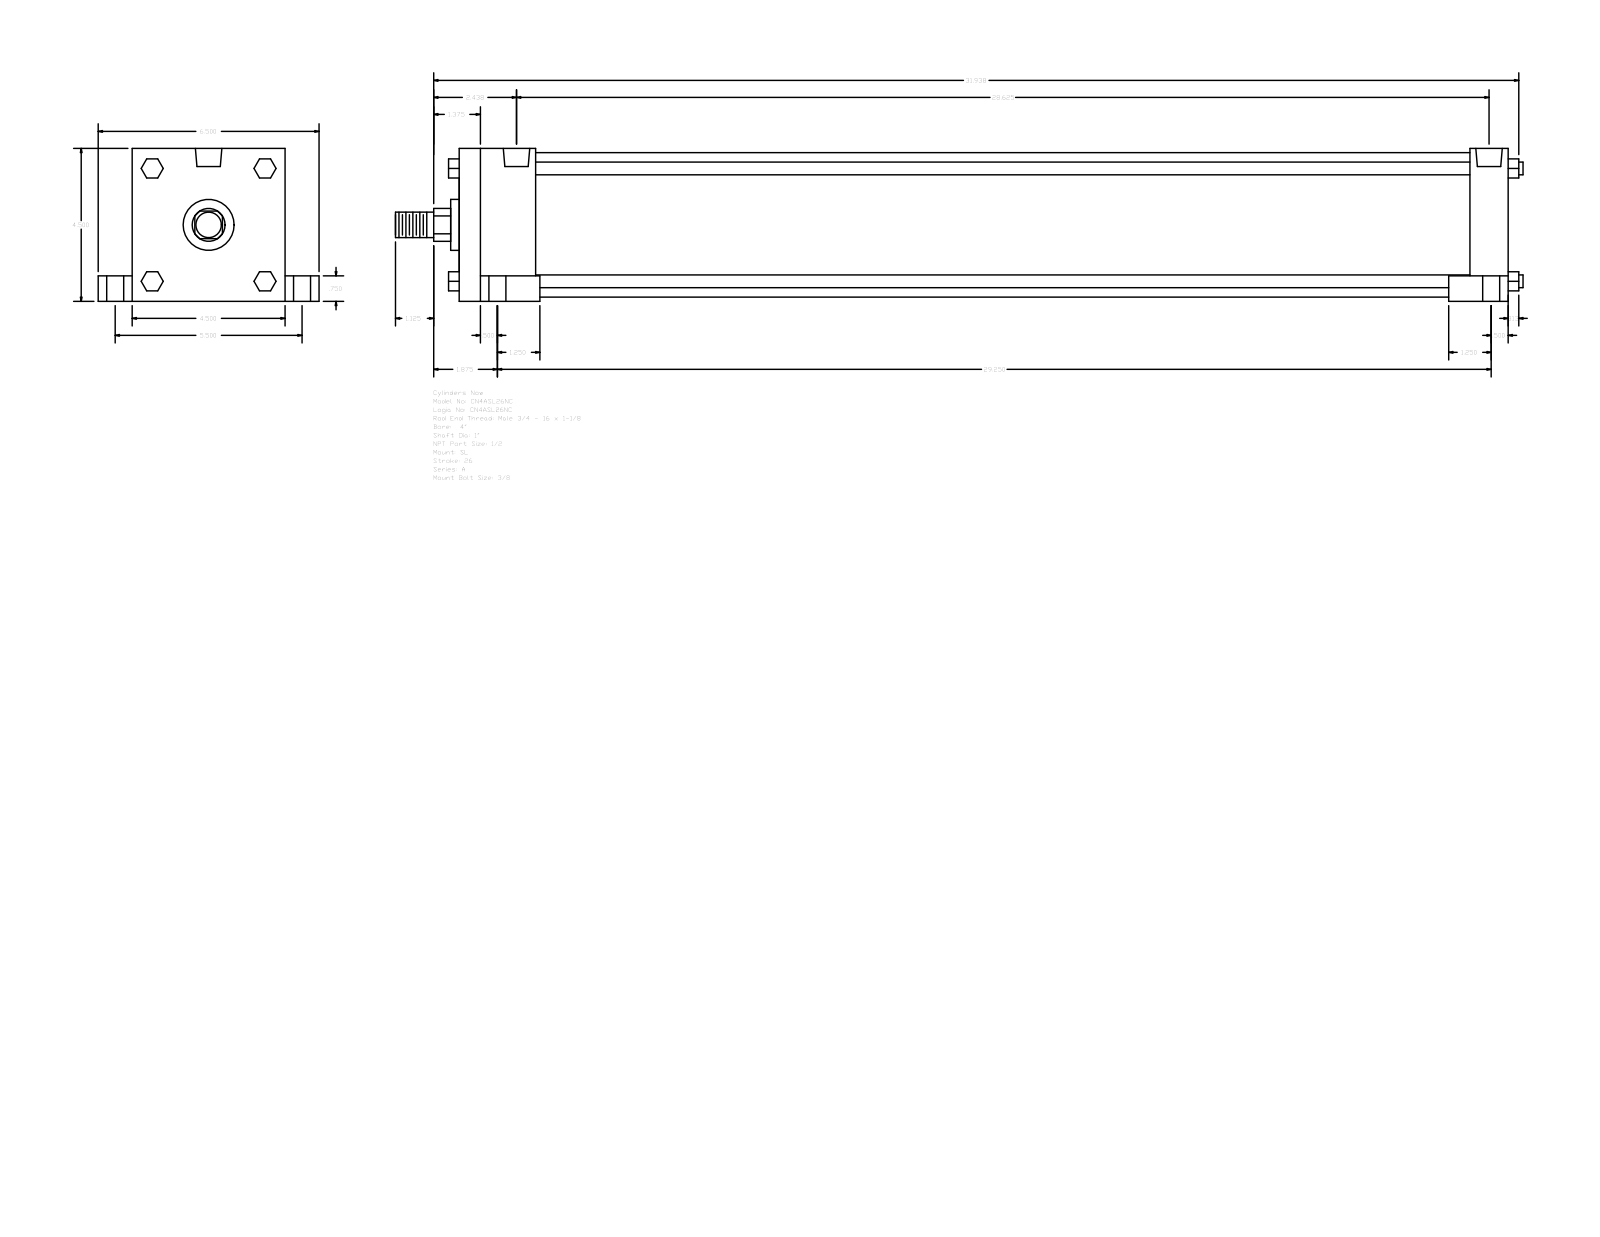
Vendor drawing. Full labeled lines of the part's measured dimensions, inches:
Part name (STEP PRODUCT): A_SL__0400_1
STEP written by: GSSL Pune (CONFIG_CONTROL_DESIGN)
Units: inches
Bodies: 0 solids, 150 faces (114 planar, 36 cylindrical, 0 other)
Overall size (bounding box): 33.187 × 6.5 × 4.5
Round holes (diameter × count): ⌀0.344 ×4, ⌀0.5 ×4, ⌀0.75 ×4, ⌀0.778 ×2
Round bosses / shafts (diameter × count): ⌀0.375 ×4, ⌀4.25 ×1, ⌀1.5 ×1, ⌀1 ×1, ⌀0.75 ×1
Partial cylindrical surfaces — rounded edges, fillets, slot ends (radius × count): R0.484 ×1
Main face-to-face distances: 4.5, 30.875, 1.125, 2.25, 28.625, 29.75, 27.5, 0.75, 1, 5.5
Hole centre spacings: 0.125, 2.751, 2.756, 2.807, 2.835, 5.5, 28.375, 28.5
